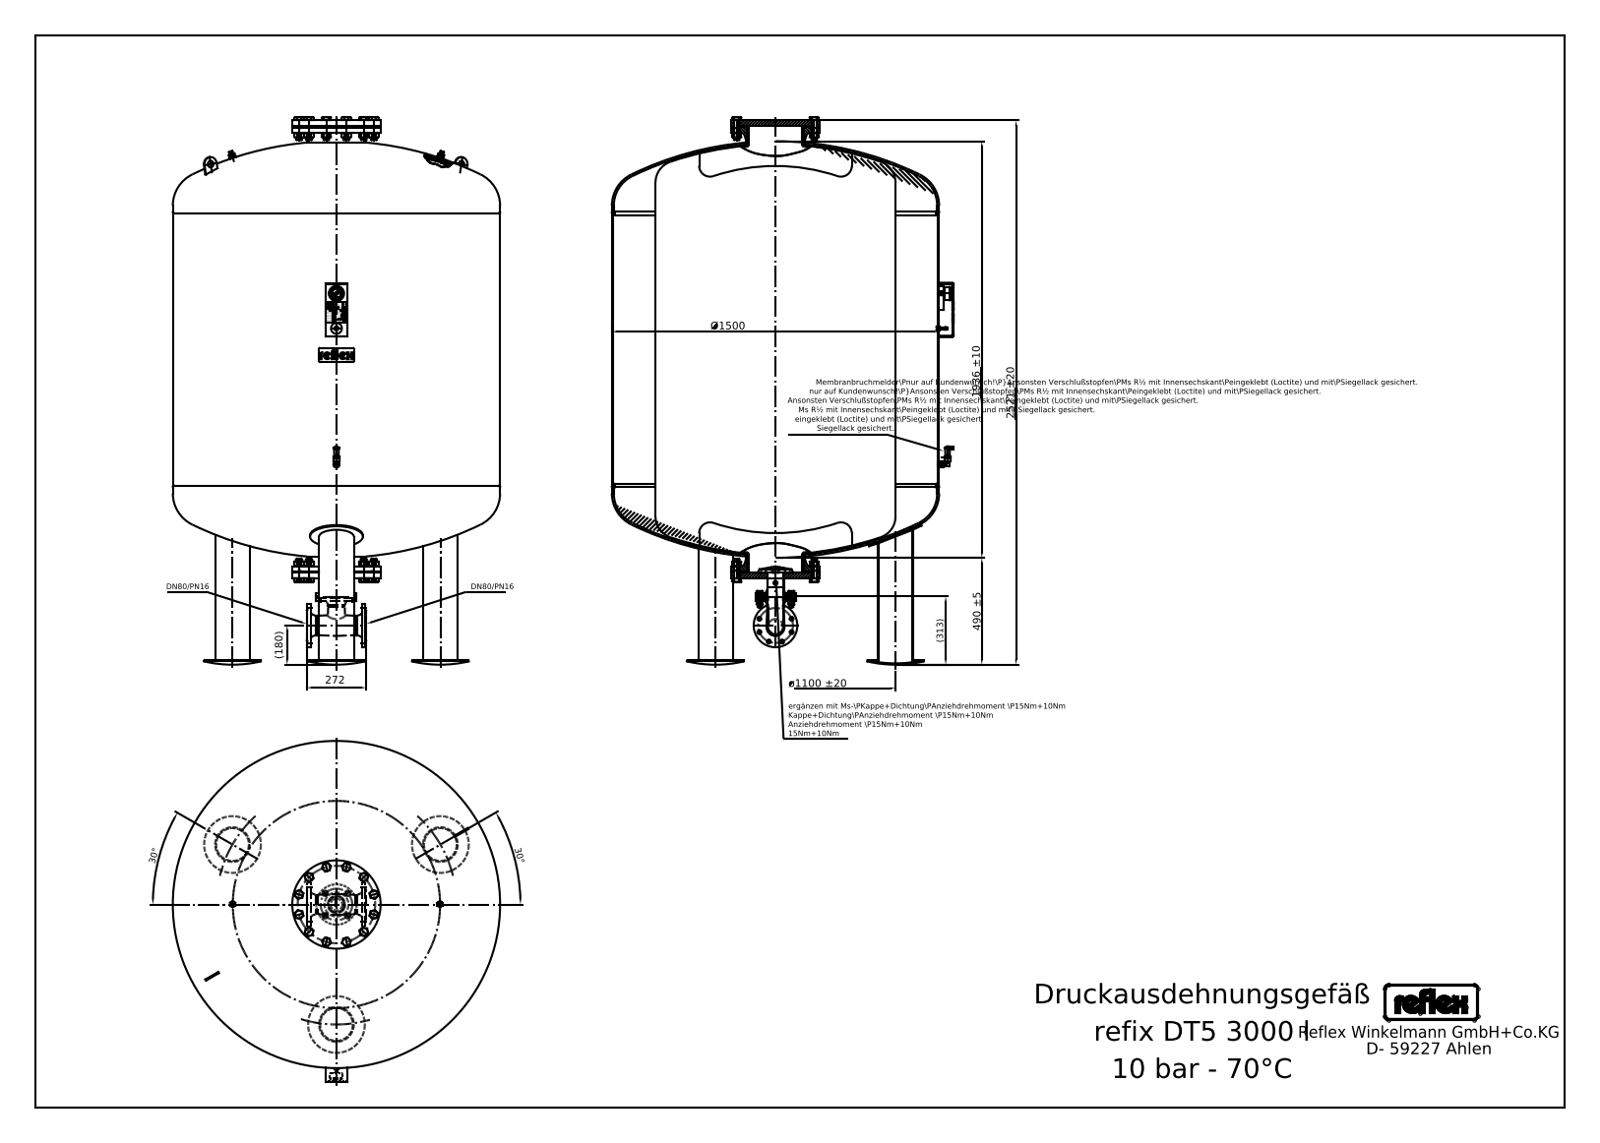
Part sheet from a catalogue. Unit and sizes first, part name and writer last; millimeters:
Units: millimetres
Overall size (bounding box): 2530 × 1566 × 1500
Round holes (diameter × count): ⌀19 ×8, ⌀10 ×1, ⌀30 ×1, ⌀50 ×1, ⌀69 ×1, ⌀88.9 ×1, ⌀260.4 ×1
Round bosses / shafts (diameter × count): ⌀16 ×16, ⌀159 ×3, ⌀28 ×2, ⌀26 ×2, ⌀20 ×2, ⌀1500 ×1, ⌀405 ×1, ⌀273 ×1
Partial cylindrical surfaces — rounded edges, fillets, slot ends (radius × count): R5.62 ×4, R2.25 ×3, R1 ×2, R3.84 ×2, R5 ×2, R6.75 ×2, R9.27 ×2, R9.4 ×2
Main face-to-face distances: 1276, 26, 2088, 31, 2057, 57, 424, 1700, 2031, 388
Hole centre spacings: 80, 113.13, 61.22, 61.24, 147.81, 147.82, 160, 82.33
Volume: 3 115 000 000 mm³ · Surface area: 21 050 000 mm²
Bodies: 28 solids, 998 faces (550 planar, 228 cylindrical, 220 other)
STEP written by: Mechanical Desktop 2008 (CONFIG_CONTROL_DESIGN)
